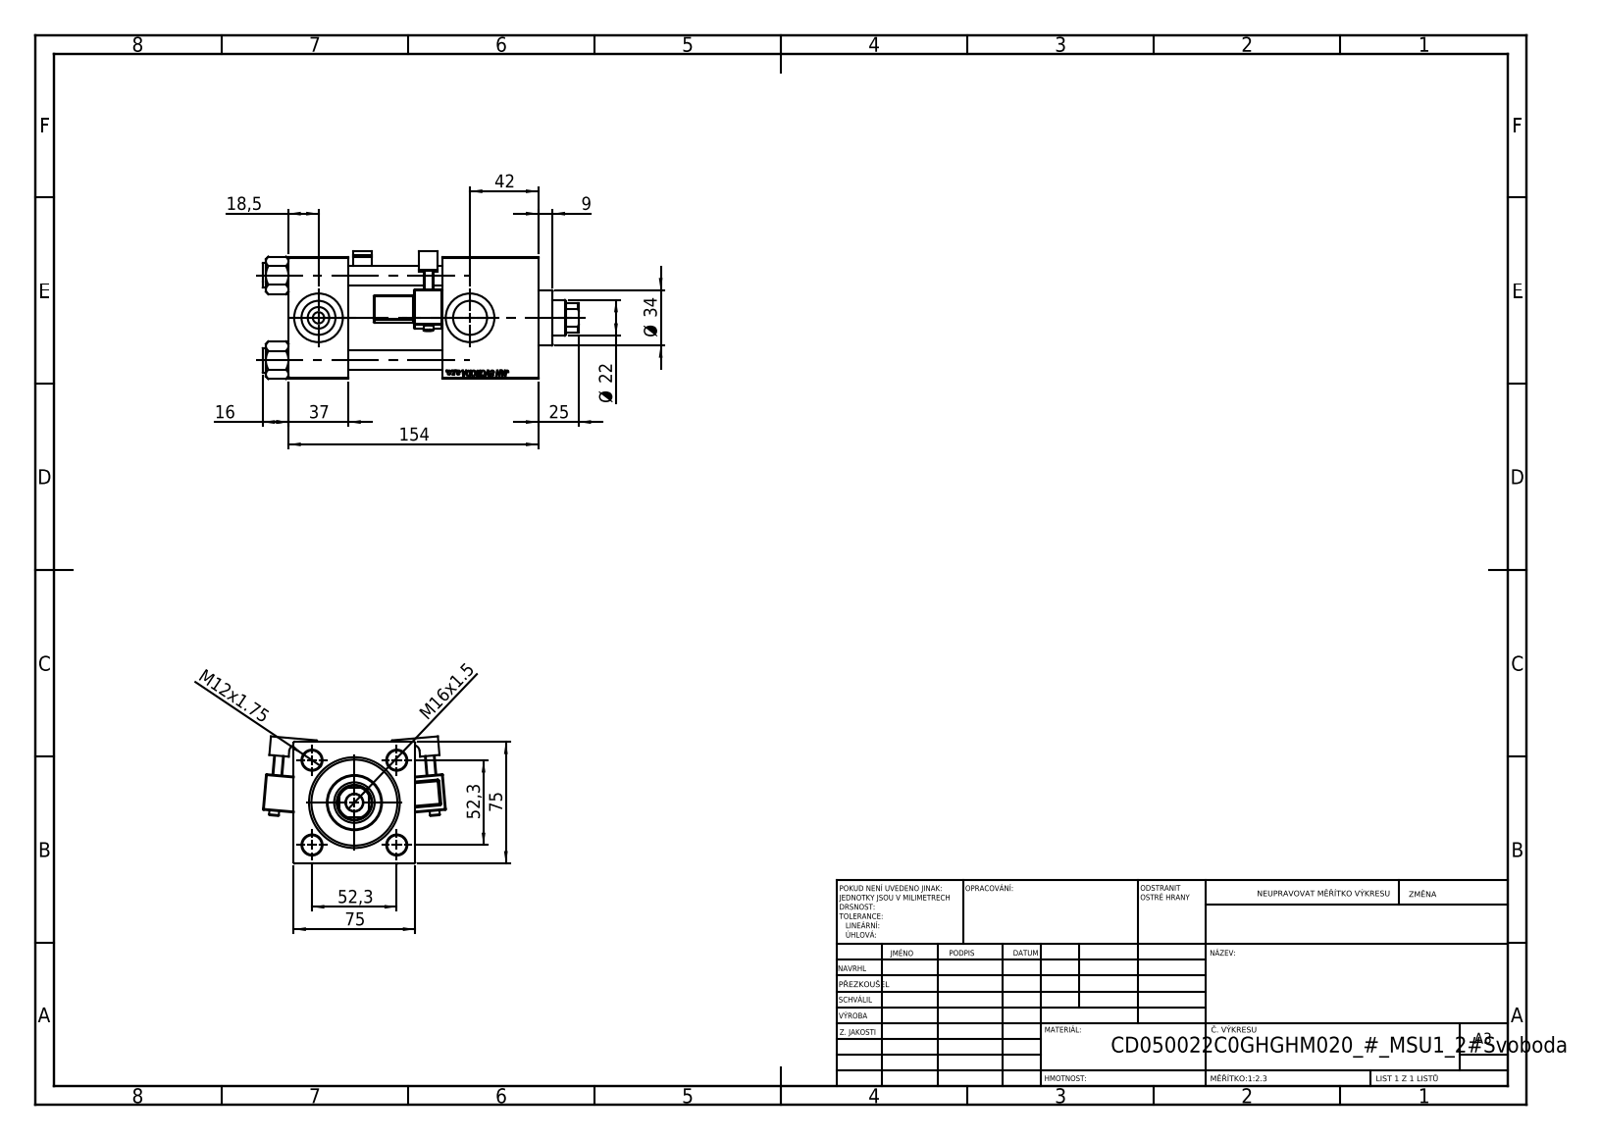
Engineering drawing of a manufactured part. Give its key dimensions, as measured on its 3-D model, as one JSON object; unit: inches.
{"part_name": "NUT_M5_V215CD_C; V215CD_VCP_C; V215CR_MSU; V215CD_Body_C (+2 more)", "step_written_by": "SolidWorks 2019 (CONFIG_CONTROL_DESIGN)", "units": "inches", "bodies": {"solids": 13, "faces": 1302, "planar": 584, "cylindrical": 146, "other": 572}, "overall_size": [7.677, 4.437, 3.095], "volume_in3": 42.6, "surface_area_in2": 247.3, "round_holes": [[0.472, 4], [0.276, 2], [0.825, 2], [1.181, 2], [0.413, 1], [0.866, 1], [0.984, 1], [1.614, 1], [1.969, 1], [2.087, 1]], "round_bosses_or_shafts": [[0.591, 4], [0.236, 2], [2.205, 1], [1.339, 1]], "partial_cylinders_radius": [[0.02, 48], [0.039, 2], [0.098, 2], [0.157, 2], [0.413, 1]], "face_to_face_distances": [2.953, 1.457, 6.063, 4.606, 3.74, 2.283, 2.323, 4.933, 3.476, 1.193], "hole_center_spacings": [1.456, 2.059, 2.912, 3.681]}
